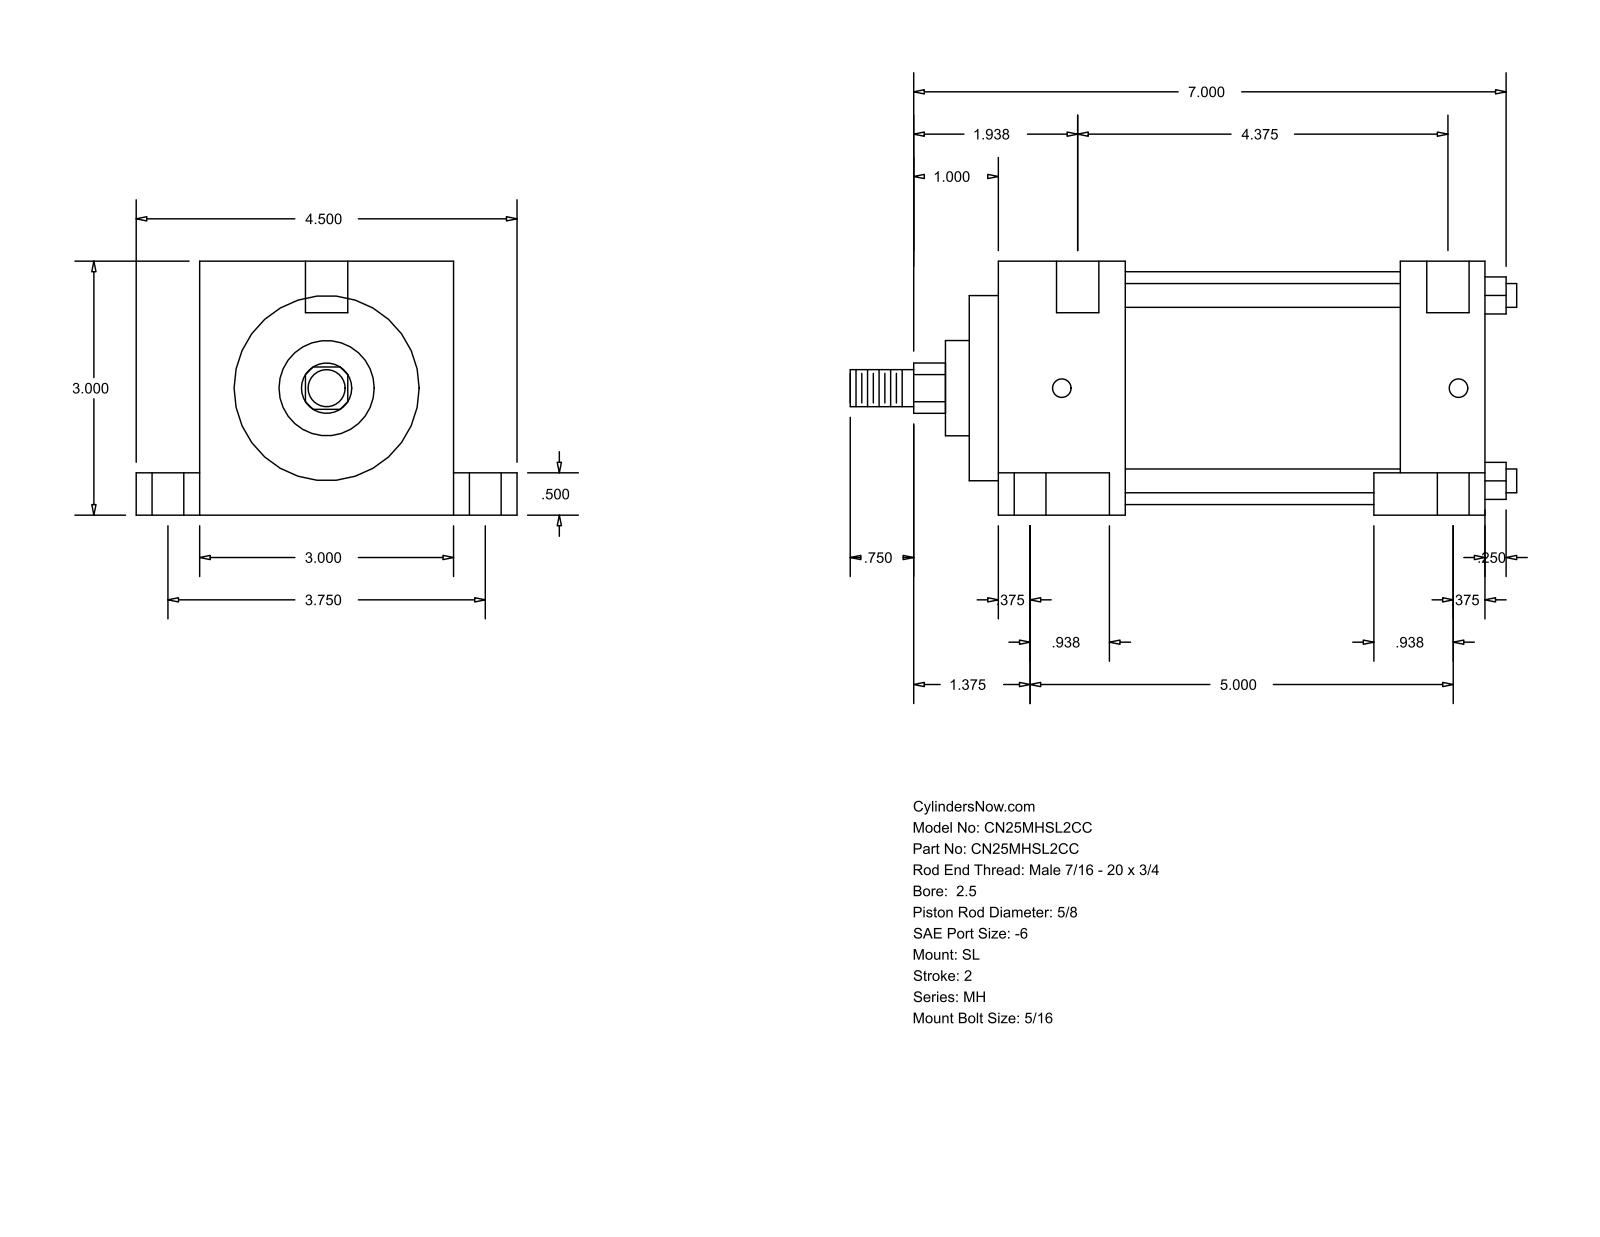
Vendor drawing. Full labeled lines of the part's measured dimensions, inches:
Part name (STEP PRODUCT): MH_SL__0250_0.625
STEP written by: GSSL Pune (CONFIG_CONTROL_DESIGN)
Units: inches
Bodies: 0 solids, 86 faces (61 planar, 25 cylindrical, 0 other)
Overall size (bounding box): 7.875 × 4.5 × 3
Round holes (diameter × count): ⌀0.219 ×2, ⌀0.375 ×2, ⌀0.625 ×2, ⌀0.5 ×1
Round bosses / shafts (diameter × count): ⌀0.281 ×4, ⌀2.75 ×1, ⌀2.187 ×1, ⌀1.125 ×1, ⌀0.625 ×1, ⌀0.437 ×1
Partial cylindrical surfaces — rounded edges, fillets, slot ends (radius × count): R0.297 ×1
Main face-to-face distances: 3, 1, 5.094, 6.094, 2.5, 0.5, 0.75, 3.75, 1.25, 4.781
Hole centre spacings: 1.876, 0.125, 3.75
